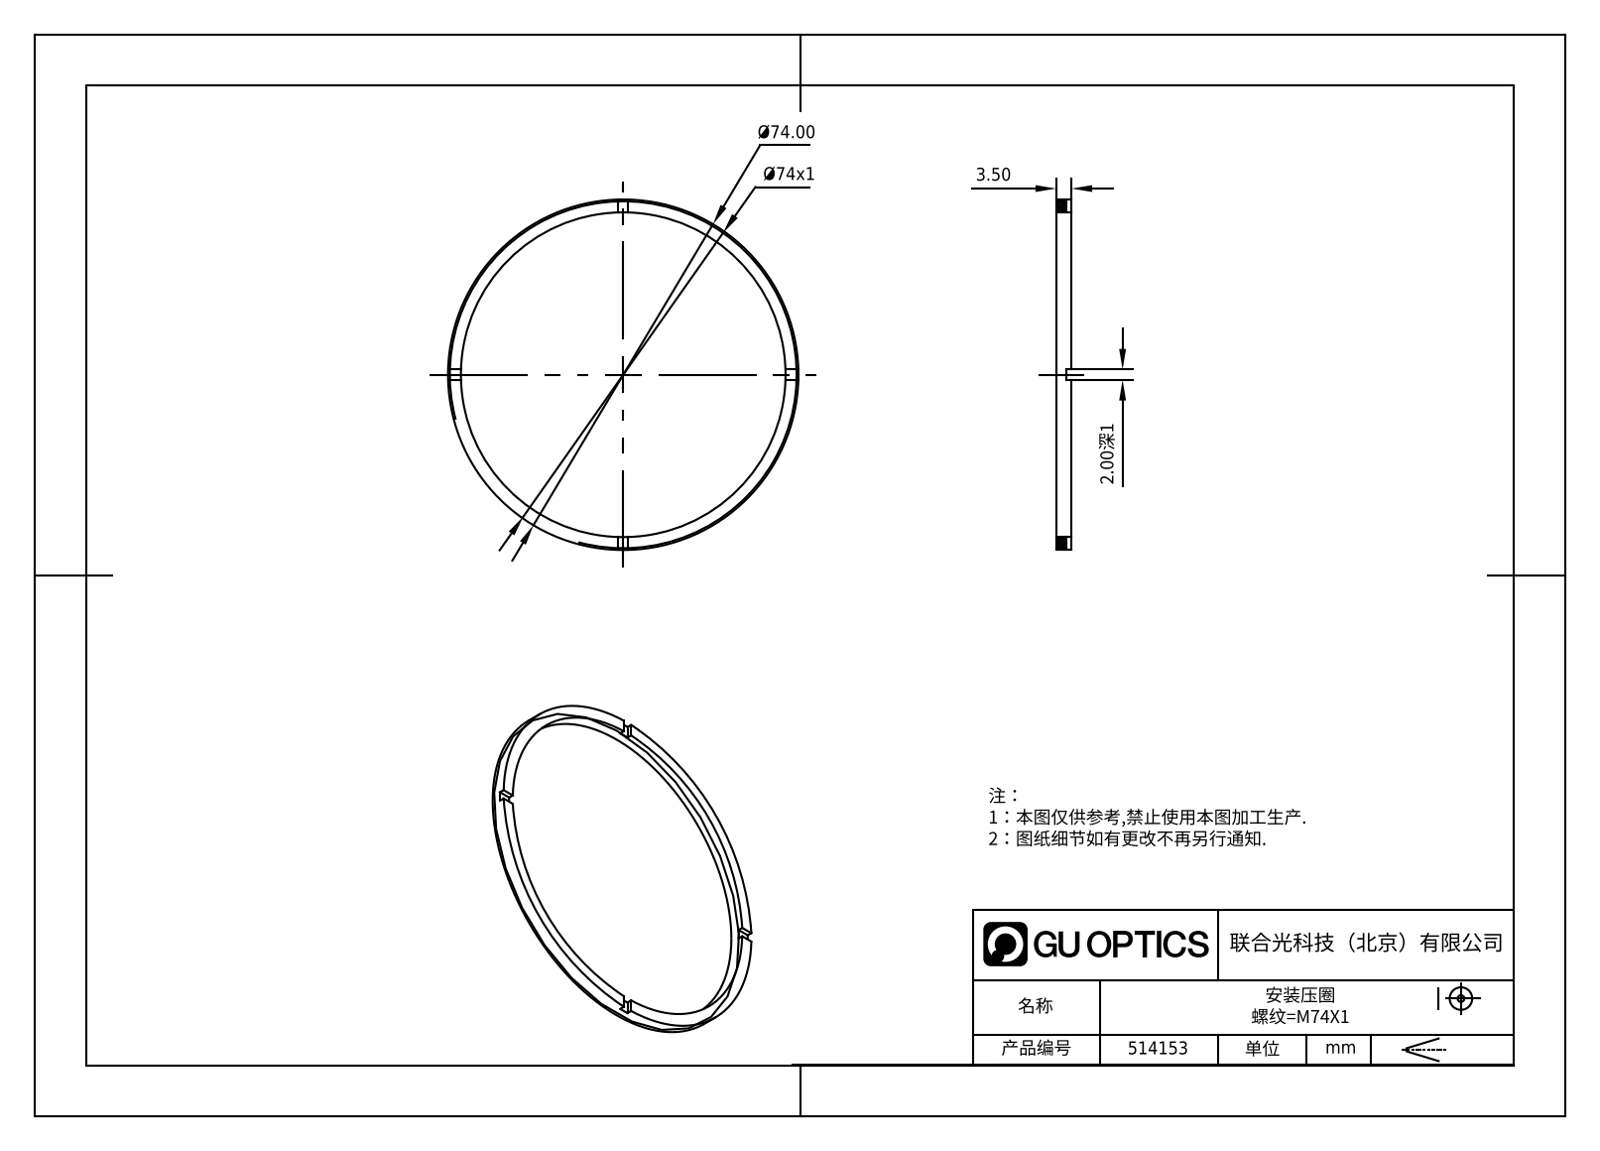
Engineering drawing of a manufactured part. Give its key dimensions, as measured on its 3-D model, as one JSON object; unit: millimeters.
{"part_name": "514153", "step_written_by": "SolidWorks 2020 (CONFIG_CONTROL_DESIGN)", "units": "millimeters", "bodies": {"solids": 1, "faces": 21, "planar": 17, "cylindrical": 4, "other": 0}, "overall_size": [74, 74, 3.5], "volume_mm3": 2318, "surface_area_mm2": 2908, "round_holes": [[68, 1]], "round_bosses_or_shafts": [[74, 1]], "face_to_face_distances": [3.5, 2.5, 1, 2]}
